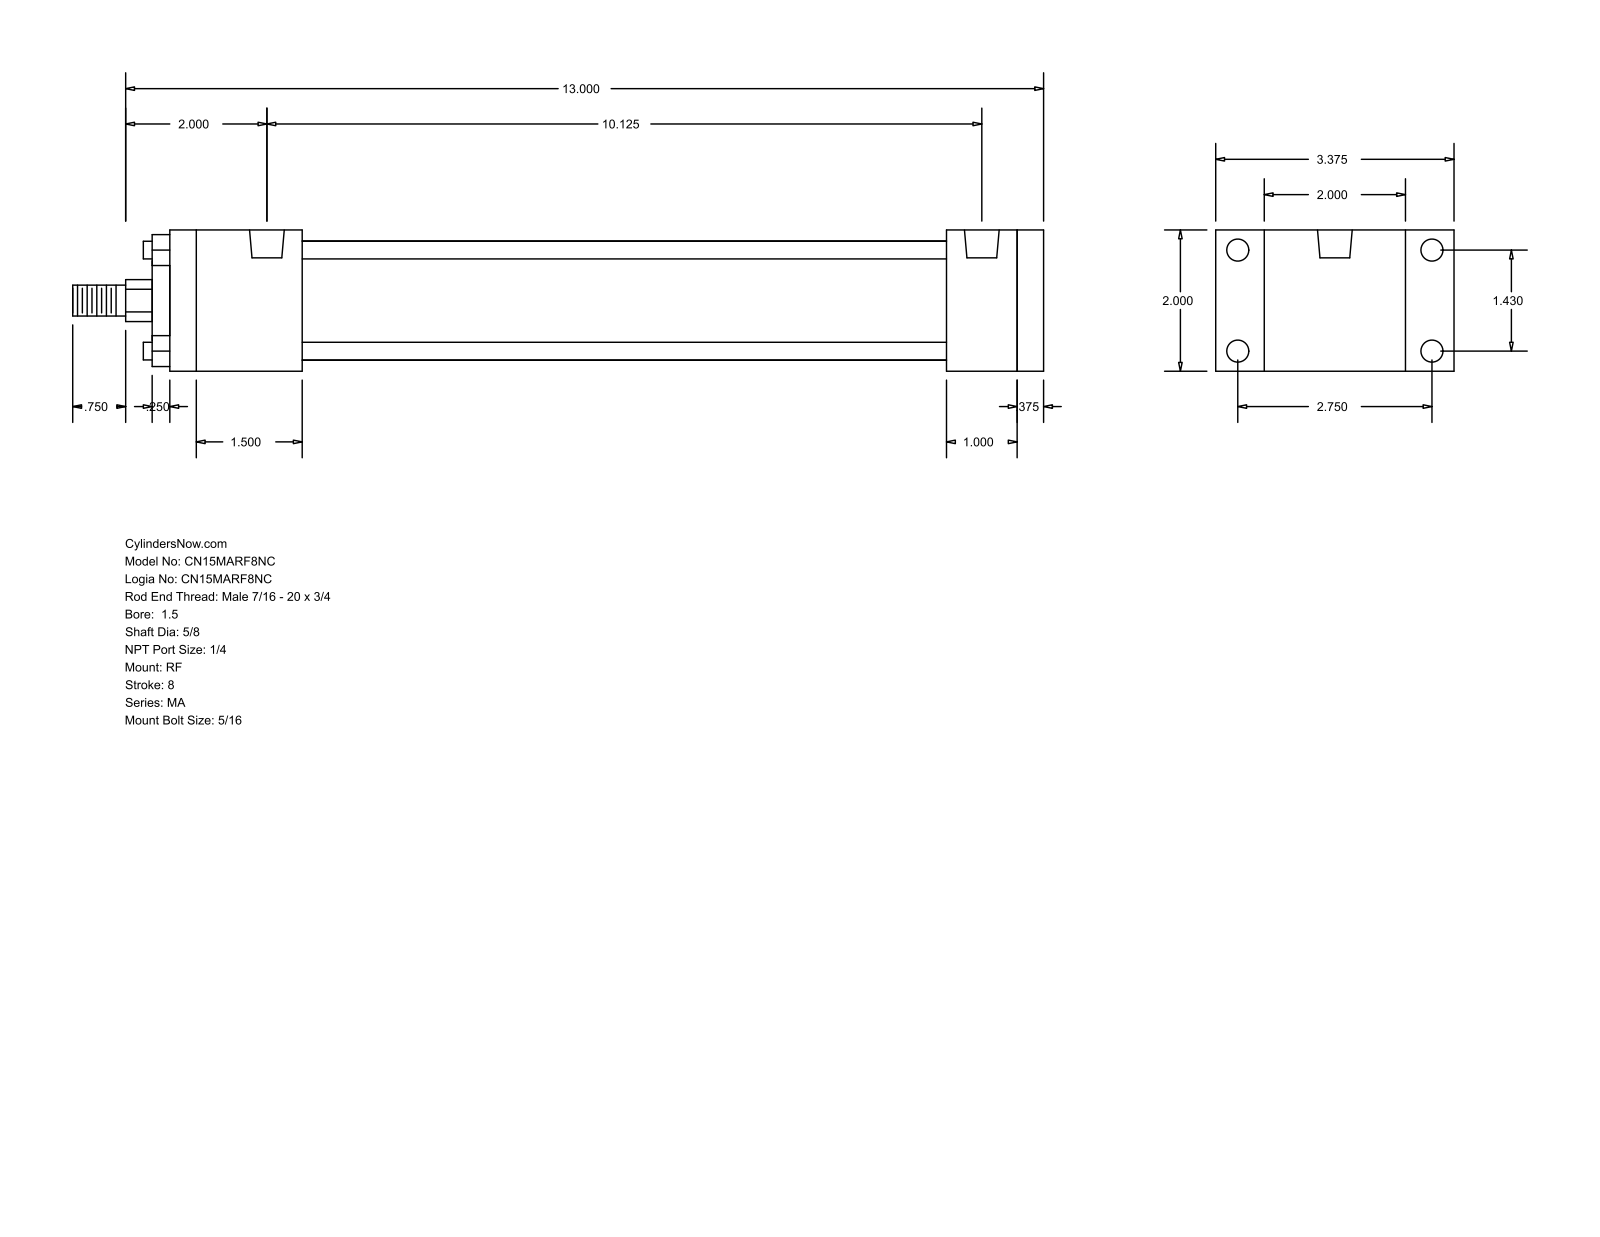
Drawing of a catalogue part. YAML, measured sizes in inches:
part_name: "MA_RF__0150_0.625"
step_written_by: "GSSL Pune (CONFIG_CONTROL_DESIGN)"
units: inches
bodies: {solids: 0, faces: 92, planar: 64, cylindrical: 28, other: 0}
overall_size: [13.75, 3.375, 2]
round_holes:
  - {diameter: 0.313, count: 8}
  - {diameter: 0.492, count: 2}
round_bosses_or_shafts:
  - {diameter: 0.25, count: 4}
  - {diameter: 1.69, count: 1}
  - {diameter: 1.125, count: 1}
  - {diameter: 0.625, count: 1}
  - {diameter: 0.437, count: 1}
partial_cylinders:
  - {radius: 0.297, count: 1}
face_to_face_distances: [2, 12.375, 0.375, 12, 1.375, 11, 1, 1.875, 9.125, 10.125]
hole_center_spacings: [1.43, 2.75, 3.099, 10.125]
